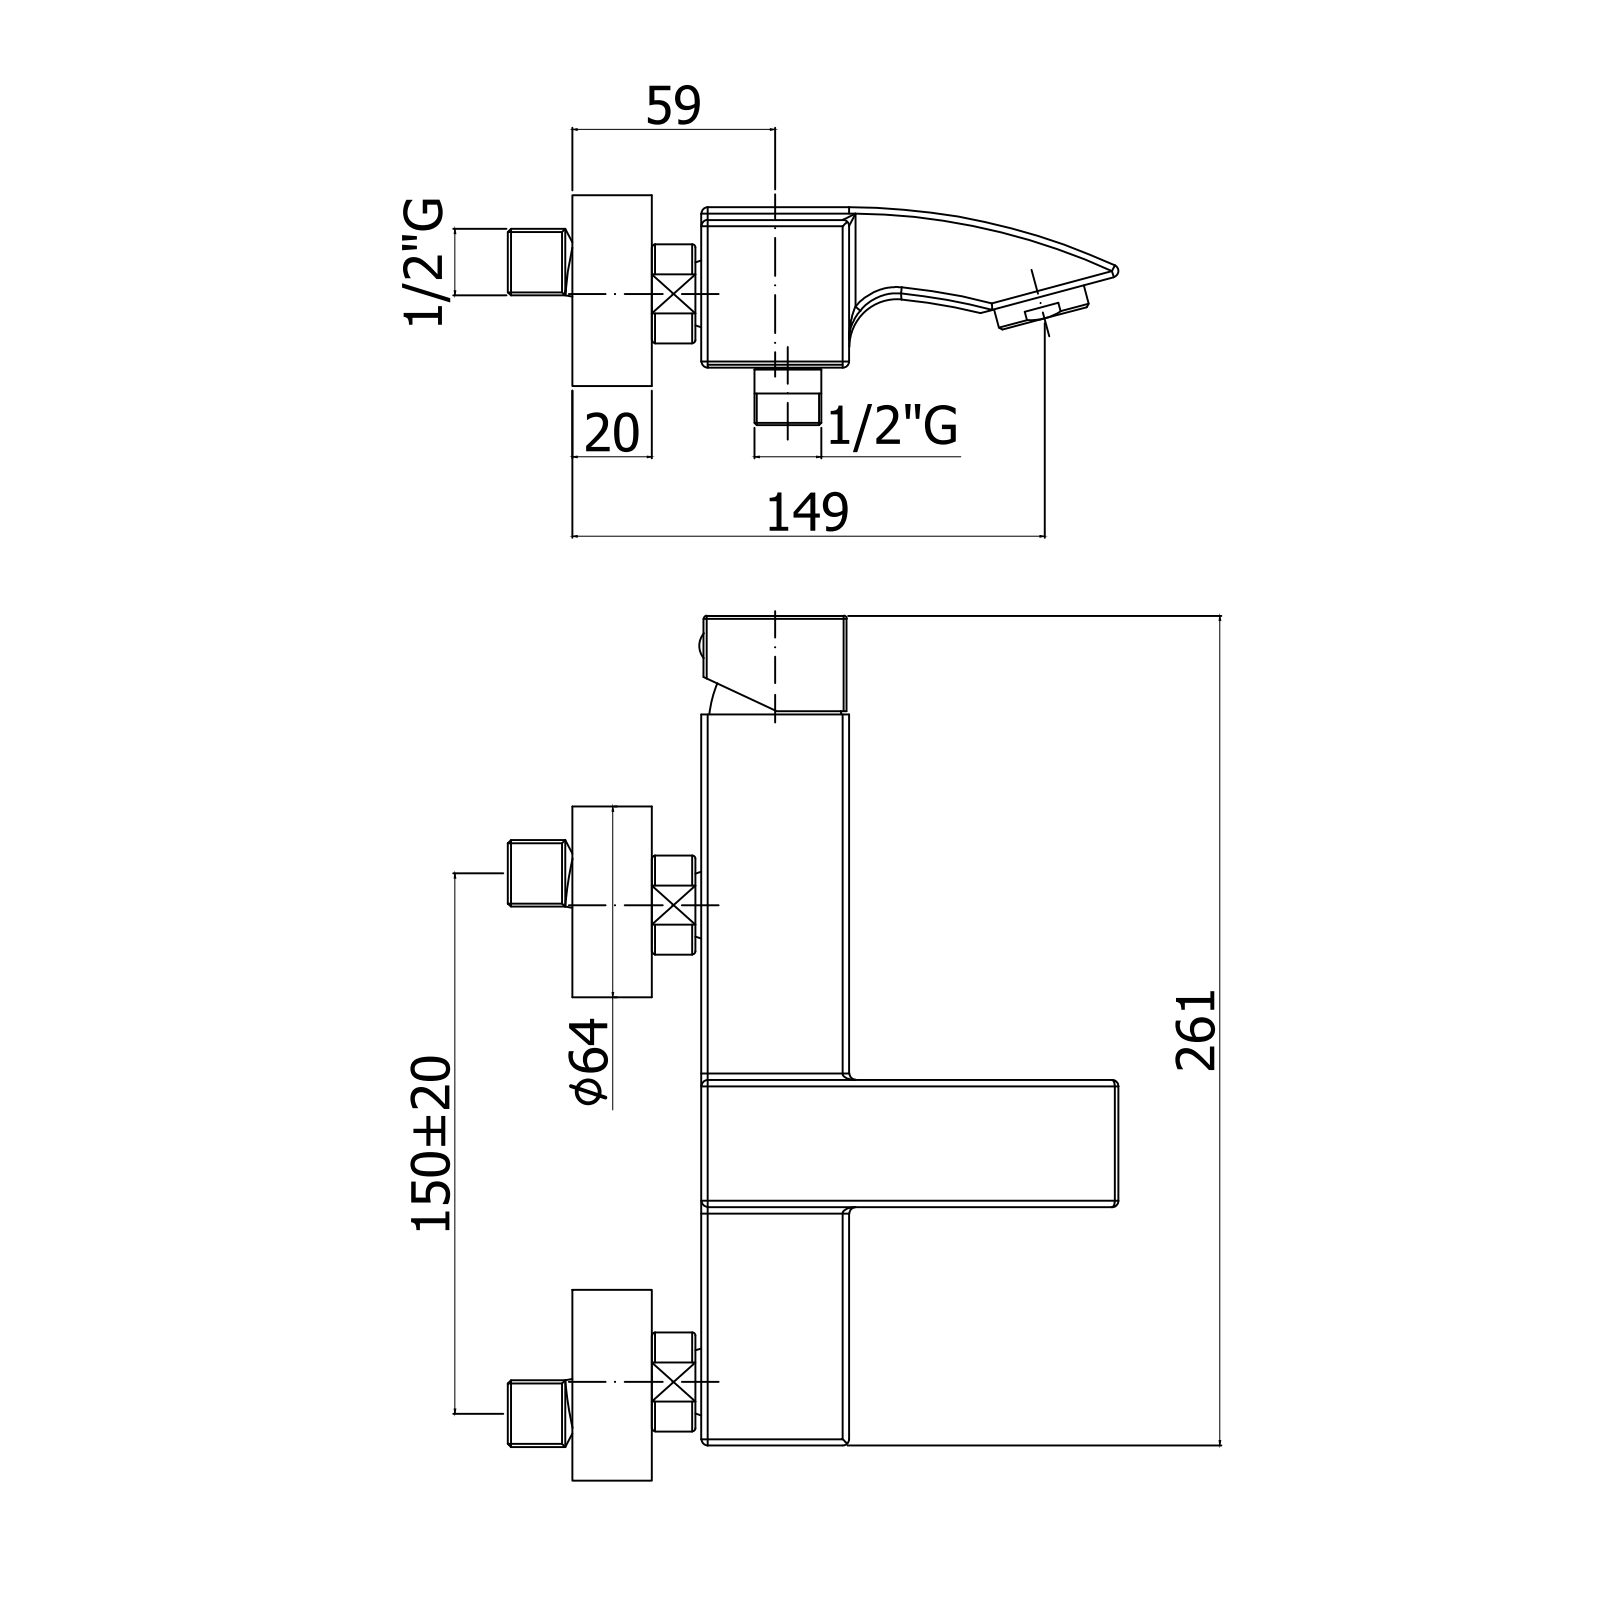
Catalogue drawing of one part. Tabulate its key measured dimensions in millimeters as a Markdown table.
| quantity | value |
| --- | --- |
| part name | LEC022CR |
| STEP written by | CREO PARAMETRIC BY PTC INC, 2020044 (CONFIG_CONTROL_DESIGN) |
| units | millimeters |
| bodies | 2 solids, 2896 faces (2235 planar, 391 cylindrical, 270 other) |
| overall size | 267.35 × 166.24 × 75 |
| volume | 350 085 mm³ |
| surface area | 201 686 mm² |
| round holes (diameter × count) | 7 × 4, 24.5 × 3, 25 × 3, 4 × 2, 10.5 × 2, 11 × 2, 16.5 × 2, 18 × 2, 21 × 2, 21.6 × 2, 28.5 × 2, 31 × 2 |
| round bosses / shafts (diameter × count) | 27 × 3, 24 × 3, 63.5 × 2, 28 × 2, 37 × 1, 35.5 × 1, 35 × 1, 34.8 × 1 |
| partial cylindrical surfaces (radius × count) | 0.5 × 27, 2 × 15, 0.15 × 11, 1 × 10, 0.3 × 4, 15.6 × 2, 3 × 1, 3.95 × 1 |
| main face-to-face distances | 3.75, 42.75, 46.5, 39, 23.25, 19.5, 3, 15, 18.75, 61.5 |
| hole center spacings | 7.07, 8.6, 11.4, 4, 6, 10, 14, 62.1 |
